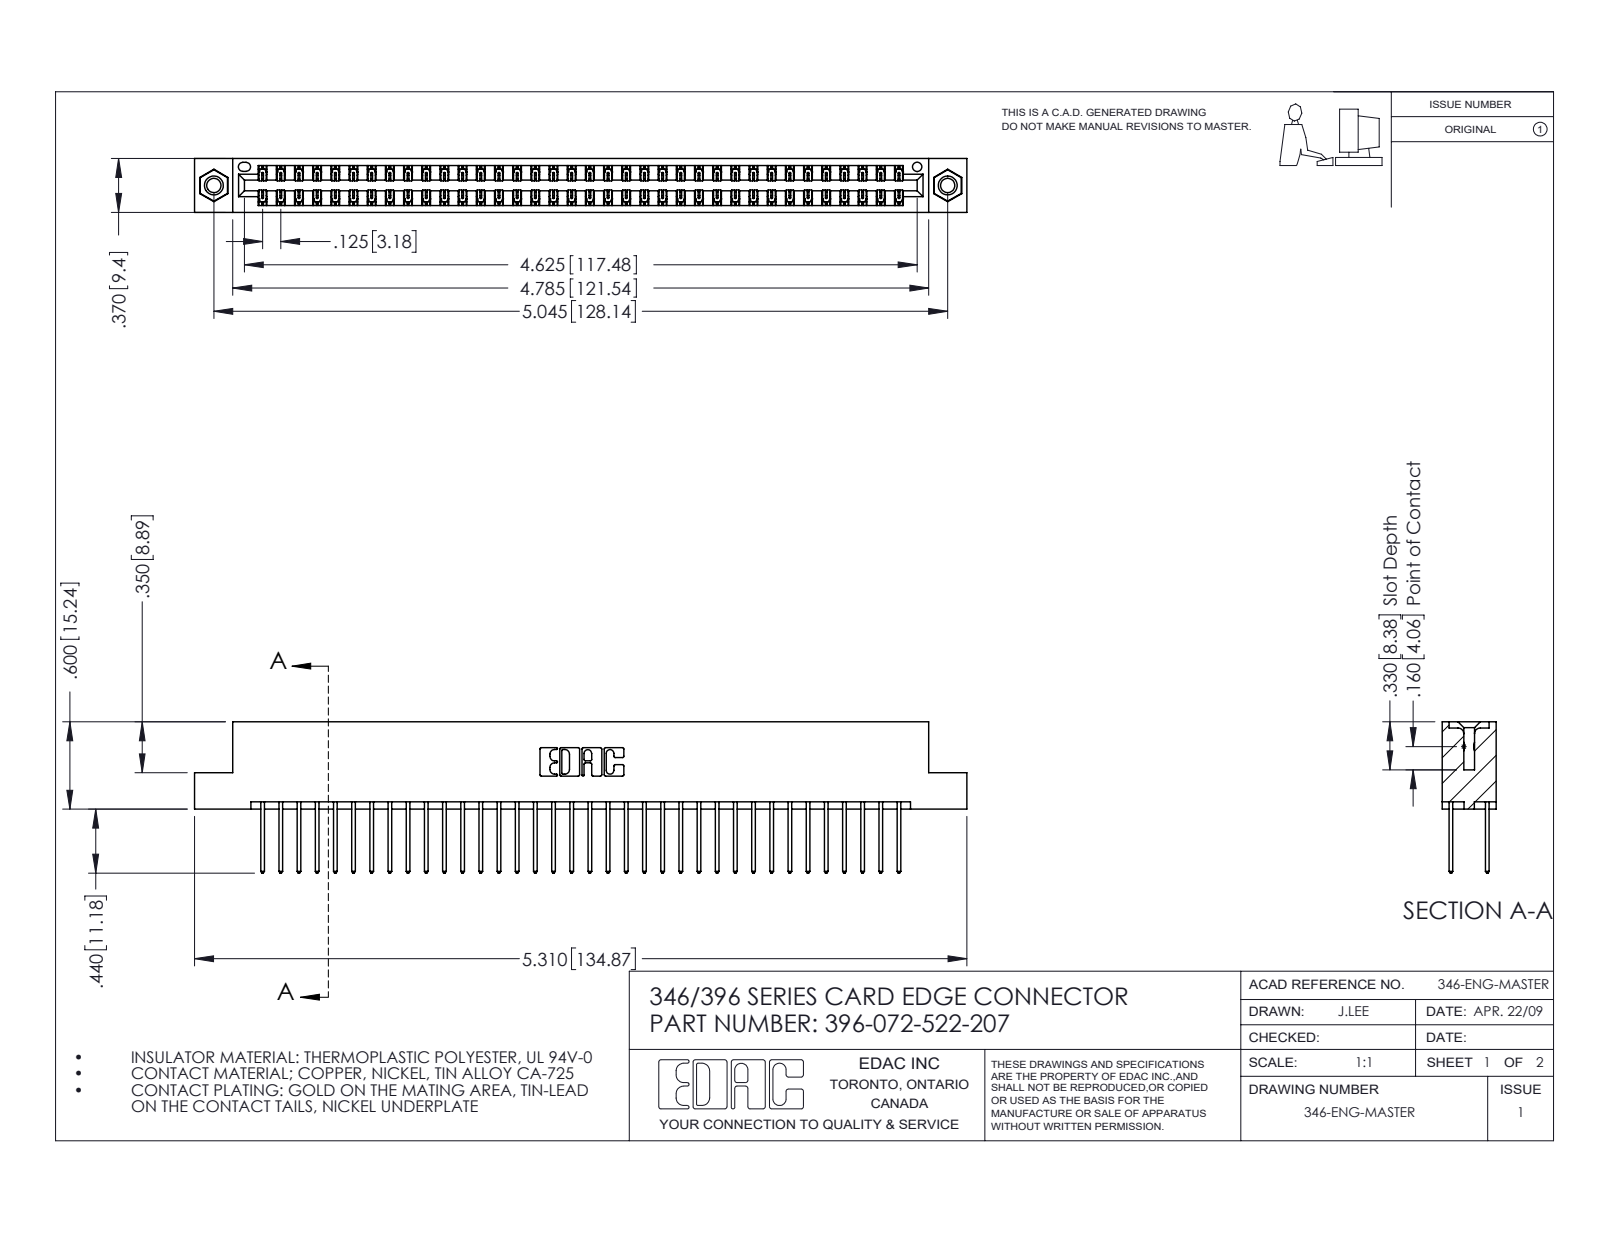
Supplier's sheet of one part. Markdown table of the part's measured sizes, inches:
| quantity | value |
| --- | --- |
| part name | 396-072-522-207; 345-292-001_345-293-122; 346 Part_Flush Mounting Lugs - 0.156 Dia-TI; 345-250-001_345-250-005-103 |
| STEP written by | SolidWorks 2016 (CONFIG_CONTROL_DESIGN) |
| units | inches |
| bodies | 75 solids, 3926 faces (2628 planar, 1282 cylindrical, 16 other) |
| overall size | 5.31 × 1.04 × 0.37 |
| volume | 0.81 in³ |
| surface area | 29.52 in² |
| round holes (diameter × count) | 0.098 × 2, 0.125 × 2, 0.156 × 2, 0.064 × 1 |
| round bosses / shafts (diameter × count) | 0.155 × 2 |
| partial cylindrical surfaces (radius × count) | 0.006 × 108, 0.01 × 72, 0.01 × 22, 0.007 × 6, 0.031 × 6, 0.026 × 3, 0.014 × 2, 0.022 × 2 |
| main face-to-face distances | 0.048, 0.322, 0.25, 0.37, 0.072, 0.298, 0.025, 0.275, 0.148, 0.222 |
| hole center spacings | 0.246, 4.836, 5.045 |
